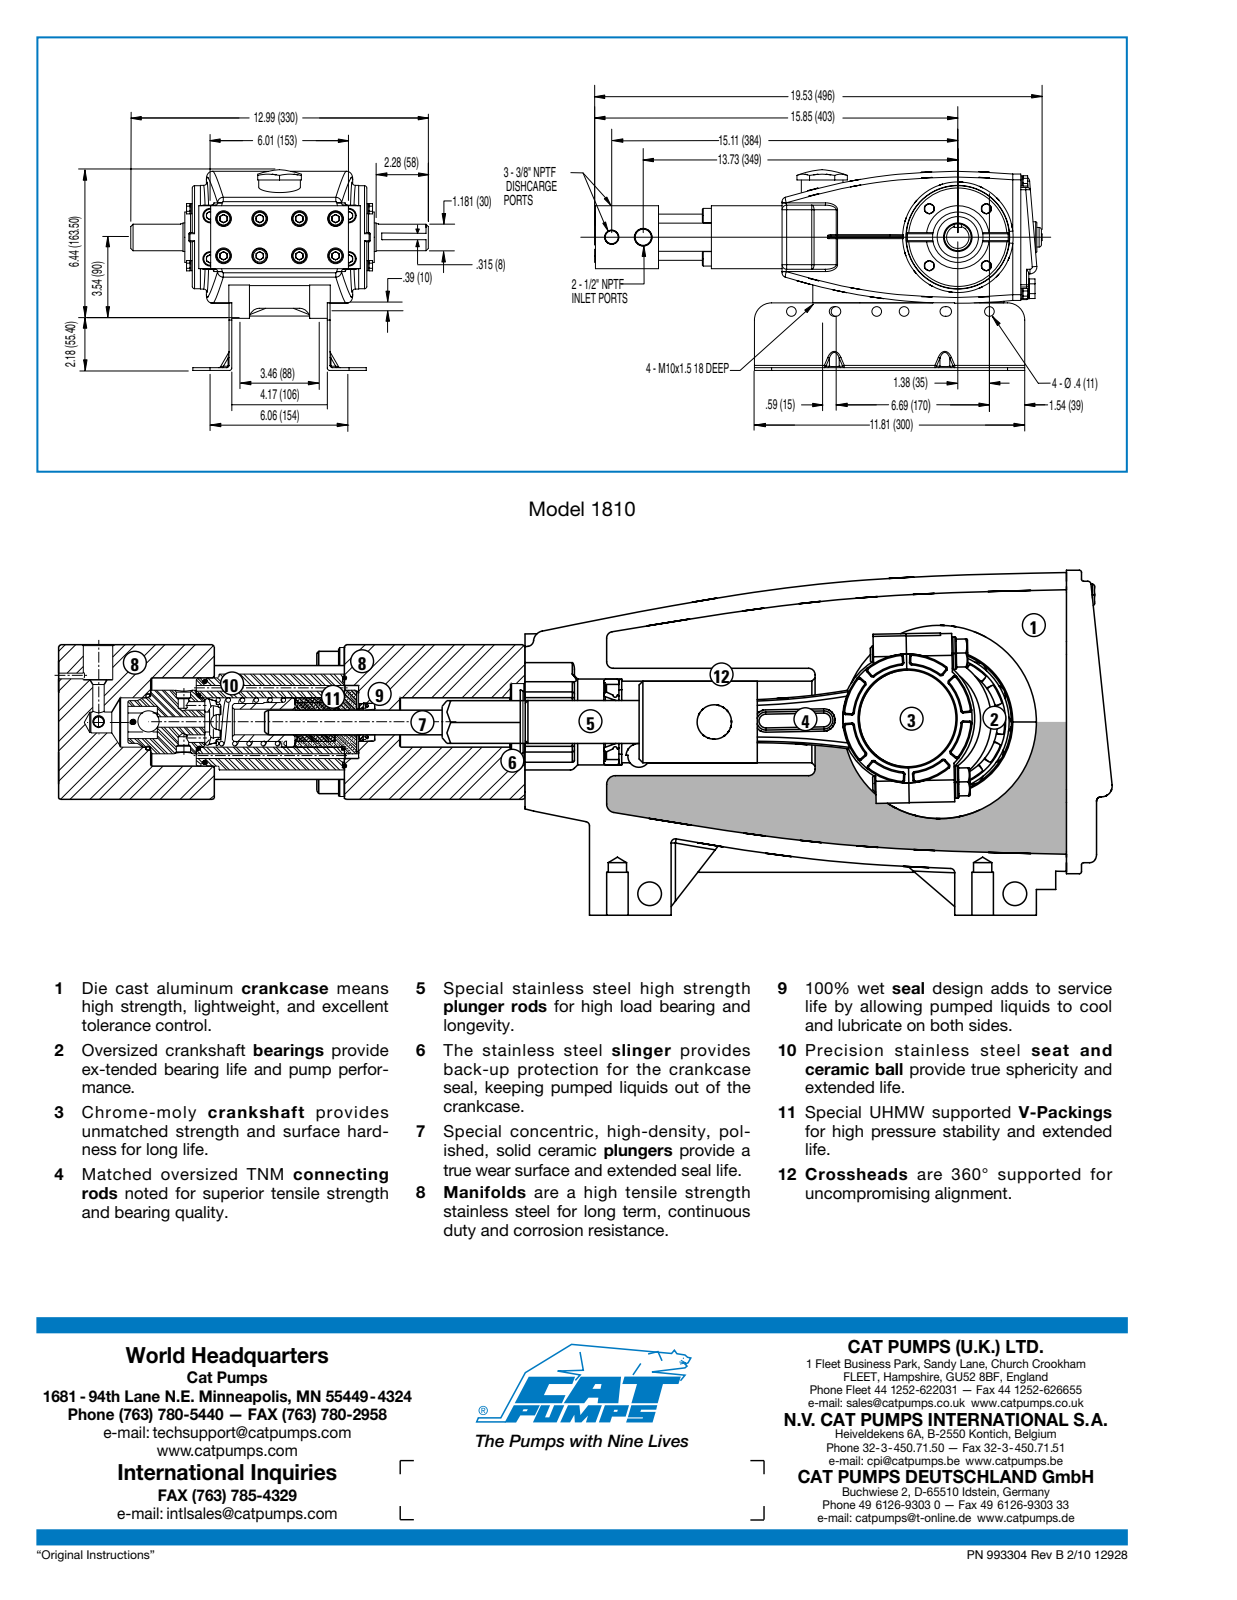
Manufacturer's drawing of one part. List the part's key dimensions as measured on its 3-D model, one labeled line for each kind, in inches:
Part name (STEP PRODUCT): 1810
STEP written by: SolidWorks 2025 (CONFIG_CONTROL_DESIGN)
Units: inches
Bodies: 0 solids, 1967 faces (681 planar, 467 cylindrical, 819 other)
Overall size (bounding box): 19.751 × 12.992 × 6.437
Round holes (diameter × count): ⌀0.669 ×8, ⌀0.335 ×6, ⌀0.433 ×6, ⌀0.315 ×4, ⌀0.327 ×4, ⌀0.343 ×4, ⌀0.413 ×4, ⌀1.25 ×3, ⌀0.256 ×2, ⌀0.562 ×2, ⌀0.118 ×1, ⌀0.193 ×1
Round bosses / shafts (diameter × count): ⌀0.63 ×16, ⌀0.394 ×8, ⌀0.748 ×4, ⌀0.551 ×4, ⌀0.455 ×4, ⌀0.453 ×4, ⌀1.7 ×3, ⌀1.57 ×3
Partial cylindrical surfaces — rounded edges, fillets, slot ends (radius × count): R0.039 ×49, R0.079 ×44, R0.433 ×10, R0.071 ×9, R0.157 ×8, R0.02 ×6, R0.059 ×4, R0.197 ×4
Main face-to-face distances: 2.75, 0.217, 7.409, 7.396, 0.23, 0.014, 7.179, 0.313, 7.313, 0.096
Hole centre spacings: 1.582, 2.067, 3.819, 0.461, 1.187, 1.187, 1.258, 1.285
